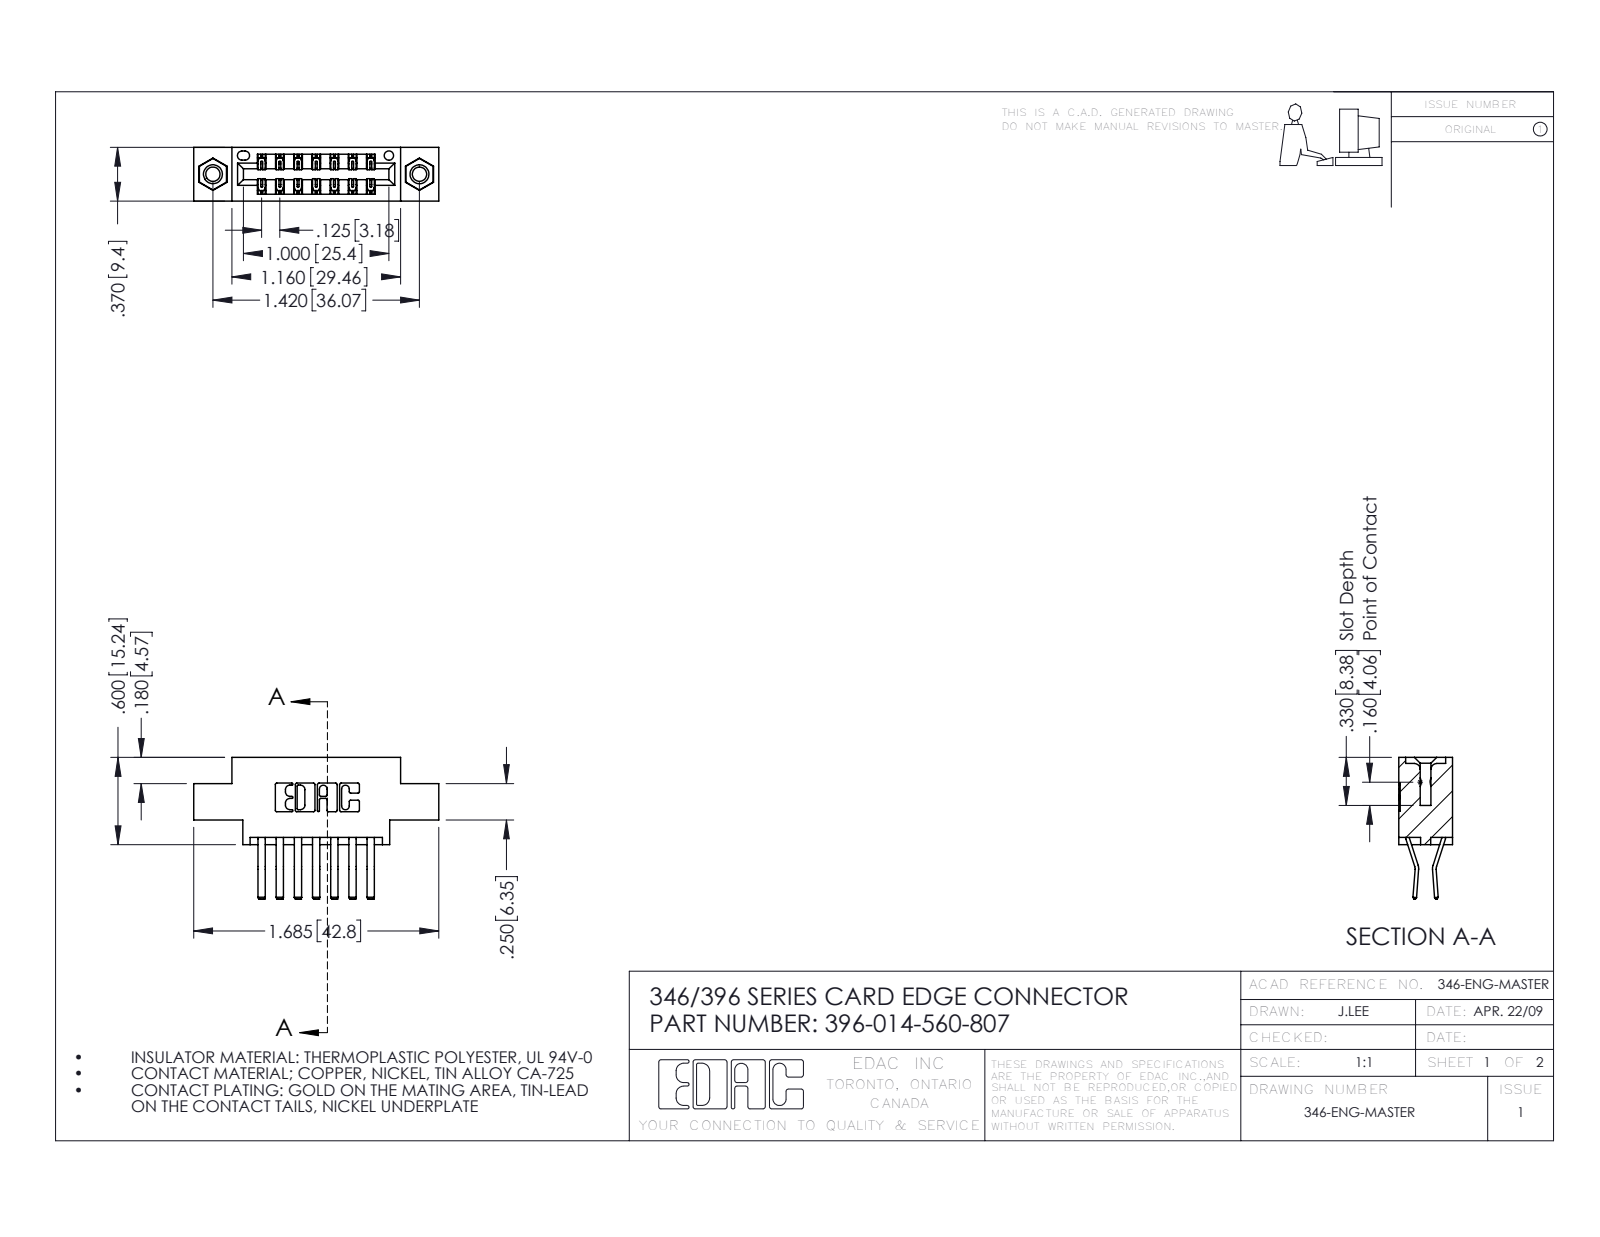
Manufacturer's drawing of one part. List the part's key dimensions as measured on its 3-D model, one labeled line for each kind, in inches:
Part name (STEP PRODUCT): 396-014-560-807; 345-250-001_345-250-005-103; 346 Part_0.170 Offset - 0.156 Dia-TI; 345-292-001_560 Tail
STEP written by: SolidWorks 2016 (CONFIG_CONTROL_DESIGN)
Units: inches
Bodies: 17 solids, 942 faces (602 planar, 324 cylindrical, 16 other)
Overall size (bounding box): 1.685 × 0.975 × 0.37
Volume: 0.233 in³ · Surface area: 8.008 in²
Round holes (diameter × count): ⌀0.098 ×2, ⌀0.125 ×2, ⌀0.156 ×2, ⌀0.064 ×1
Round bosses / shafts (diameter × count): ⌀0.155 ×2
Partial cylindrical surfaces — rounded edges, fillets, slot ends (radius × count): R0.01 ×22, R0.006 ×21, R0.007 ×6, R0.031 ×6, R0.026 ×3, R0.01 ×2, R0.014 ×2, R0.022 ×2
Main face-to-face distances: 0.25, 0.37, 0.048, 0.322, 0.025, 0.222, 0.148, 0.1, 0.174, 0.072
Hole centre spacings: 0.246, 1.217, 1.42
